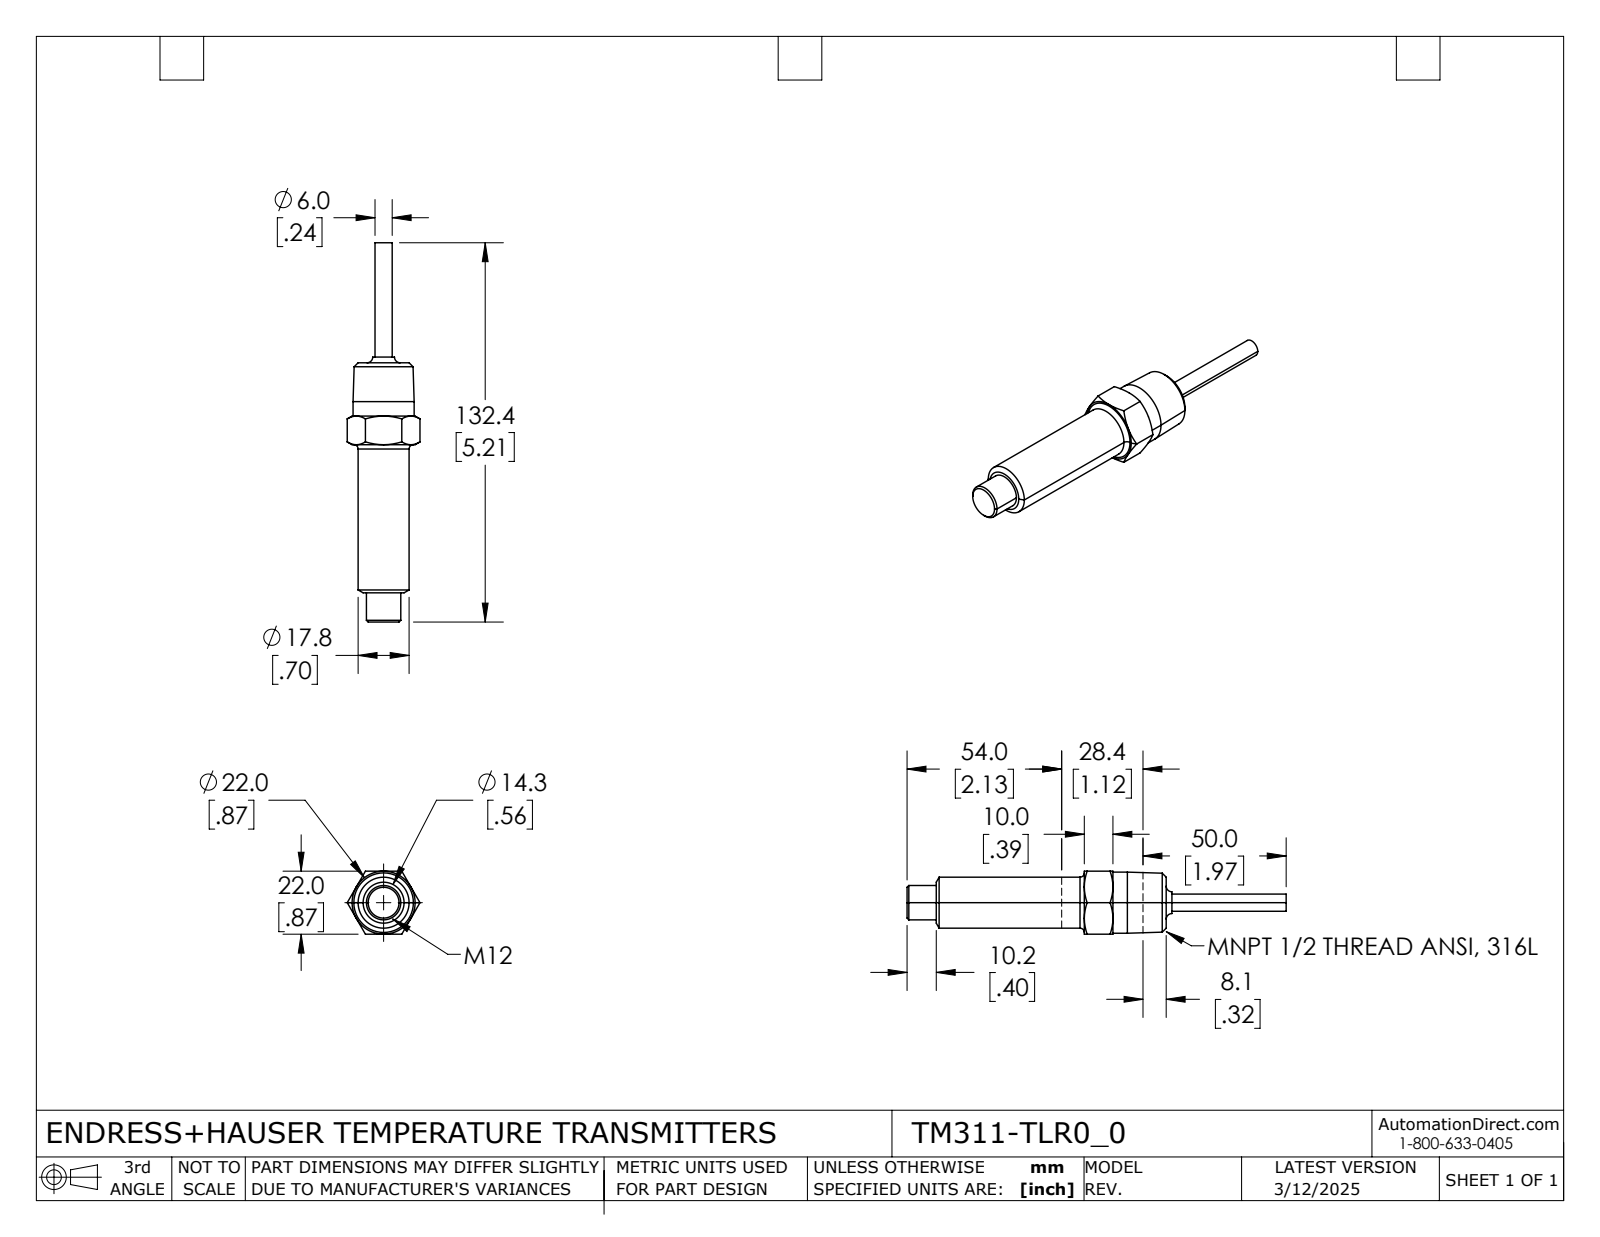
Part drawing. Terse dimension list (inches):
name: TM311-TLR0_0
written by: SolidWorks 2021 (AUTOMOTIVE_DESIGN)
unit: in
bodies: 1 solid, 49 faces (13 planar, 8 cylindrical, 28 other)
size: 5.213 × 1 × 0.866
volume: 1.575 in³; area: 10.35 in²
bosses: 1× ⌀0.84, 1× ⌀0.701, 1× ⌀0.472, 1× ⌀0.236
face distances: 0.866, 3.563, 3.161, 0.402, 1.126, 2.035, 2.437, 1.65, 2.776, 4.811
